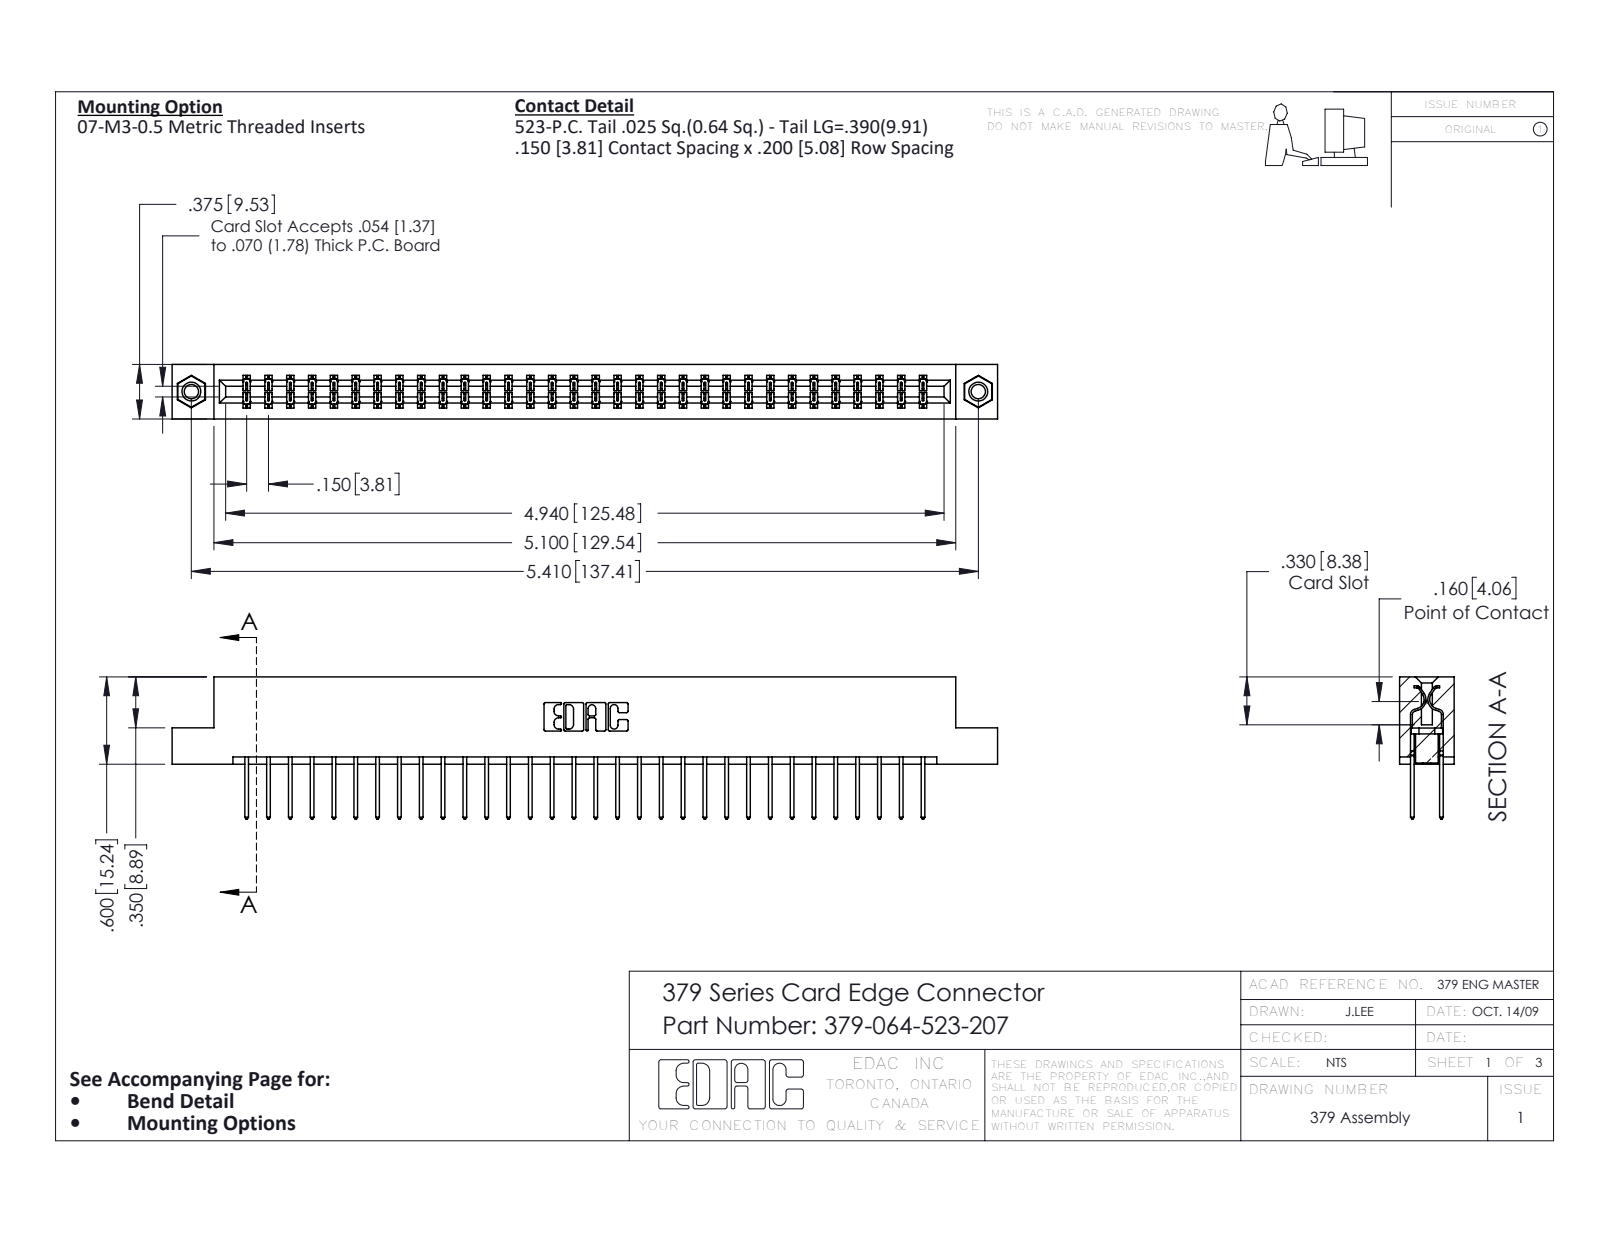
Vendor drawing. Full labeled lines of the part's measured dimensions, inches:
Part name (STEP PRODUCT): 345-292-001_345-293-123; 345-250-001_345-250-005-103; 379 Part_Flush - .156 Dia - TI; 379-064-523-207
STEP written by: SolidWorks 2016 (CONFIG_CONTROL_DESIGN)
Units: inches
Bodies: 67 solids, 3502 faces (2406 planar, 1080 cylindrical, 16 other)
Overall size (bounding box): 5.675 × 0.977 × 0.375
Volume: 0.937 in³ · Surface area: 27.61 in²
Round holes (diameter × count): ⌀0.098 ×2, ⌀0.125 ×2, ⌀0.156 ×2
Round bosses / shafts (diameter × count): ⌀0.155 ×2
Partial cylindrical surfaces — rounded edges, fillets, slot ends (radius × count): R0.006 ×96, R0.01 ×64, R0.01 ×22, R0.007 ×6, R0.031 ×6, R0.026 ×3, R0.014 ×2, R0.022 ×2
Main face-to-face distances: 0.3, 0.075, 0.375, 0.2, 0.1, 0.275, 0.225, 0.025, 0.15, 0.076
Hole centre spacings: 5.41
